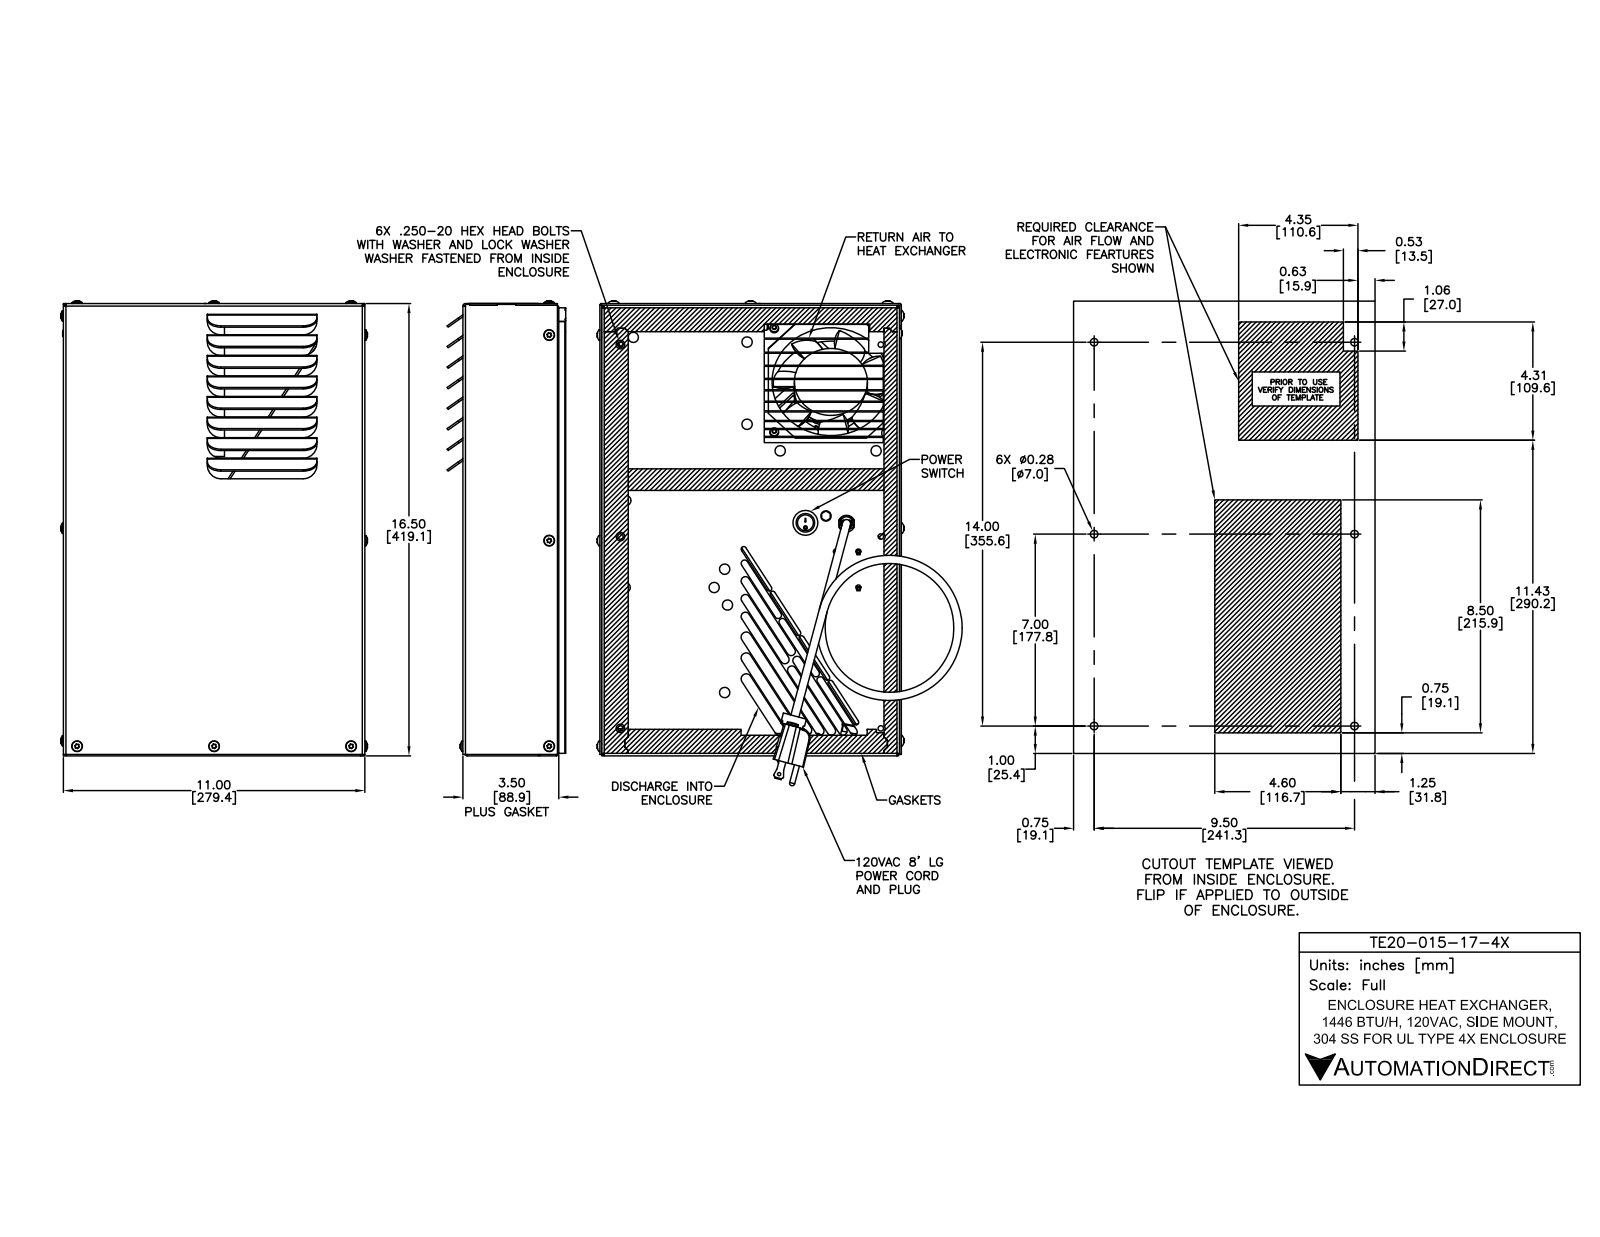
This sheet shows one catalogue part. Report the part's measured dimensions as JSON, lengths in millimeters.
{"part_name": "TE20-015-17-4X", "step_written_by": "SolidWorks 2017 (AUTOMOTIVE_DESIGN)", "units": "millimeters", "bodies": {"solids": 66, "faces": 2808, "planar": 1639, "cylindrical": 897, "other": 272}, "overall_size": [449.5, 339.1, 191.1], "volume_mm3": 2283000, "surface_area_mm2": 1544000, "round_holes": [[4.9, 21], [5.6, 20], [5.2, 11], [3.5, 8], [4.1, 8], [4.5, 8], [12.7, 8], [2.8, 6], [5.1, 6], [4, 4], [5.4, 4], [7.9, 3]], "round_bosses_or_shafts": [[9.3, 13], [4.3, 13], [8, 8], [7.9, 8], [4.7, 8], [4.2, 8], [3.3, 8], [8.3, 6]], "partial_cylinders_radius": [[0.5, 79], [0.5, 78], [0.8, 54], [2.4, 48], [0.6, 38], [1.5, 28], [0.8, 18], [0.6, 16]], "face_to_face_distances": [1.6, 87.3, 1.6, 85.8, 88.9, 276.1, 277.7, 6.4, 1.7, 95.3], "hole_center_spacings": [105, 31.8, 148.5, 74.2, 148.5, 105, 74.2, 28.6]}
